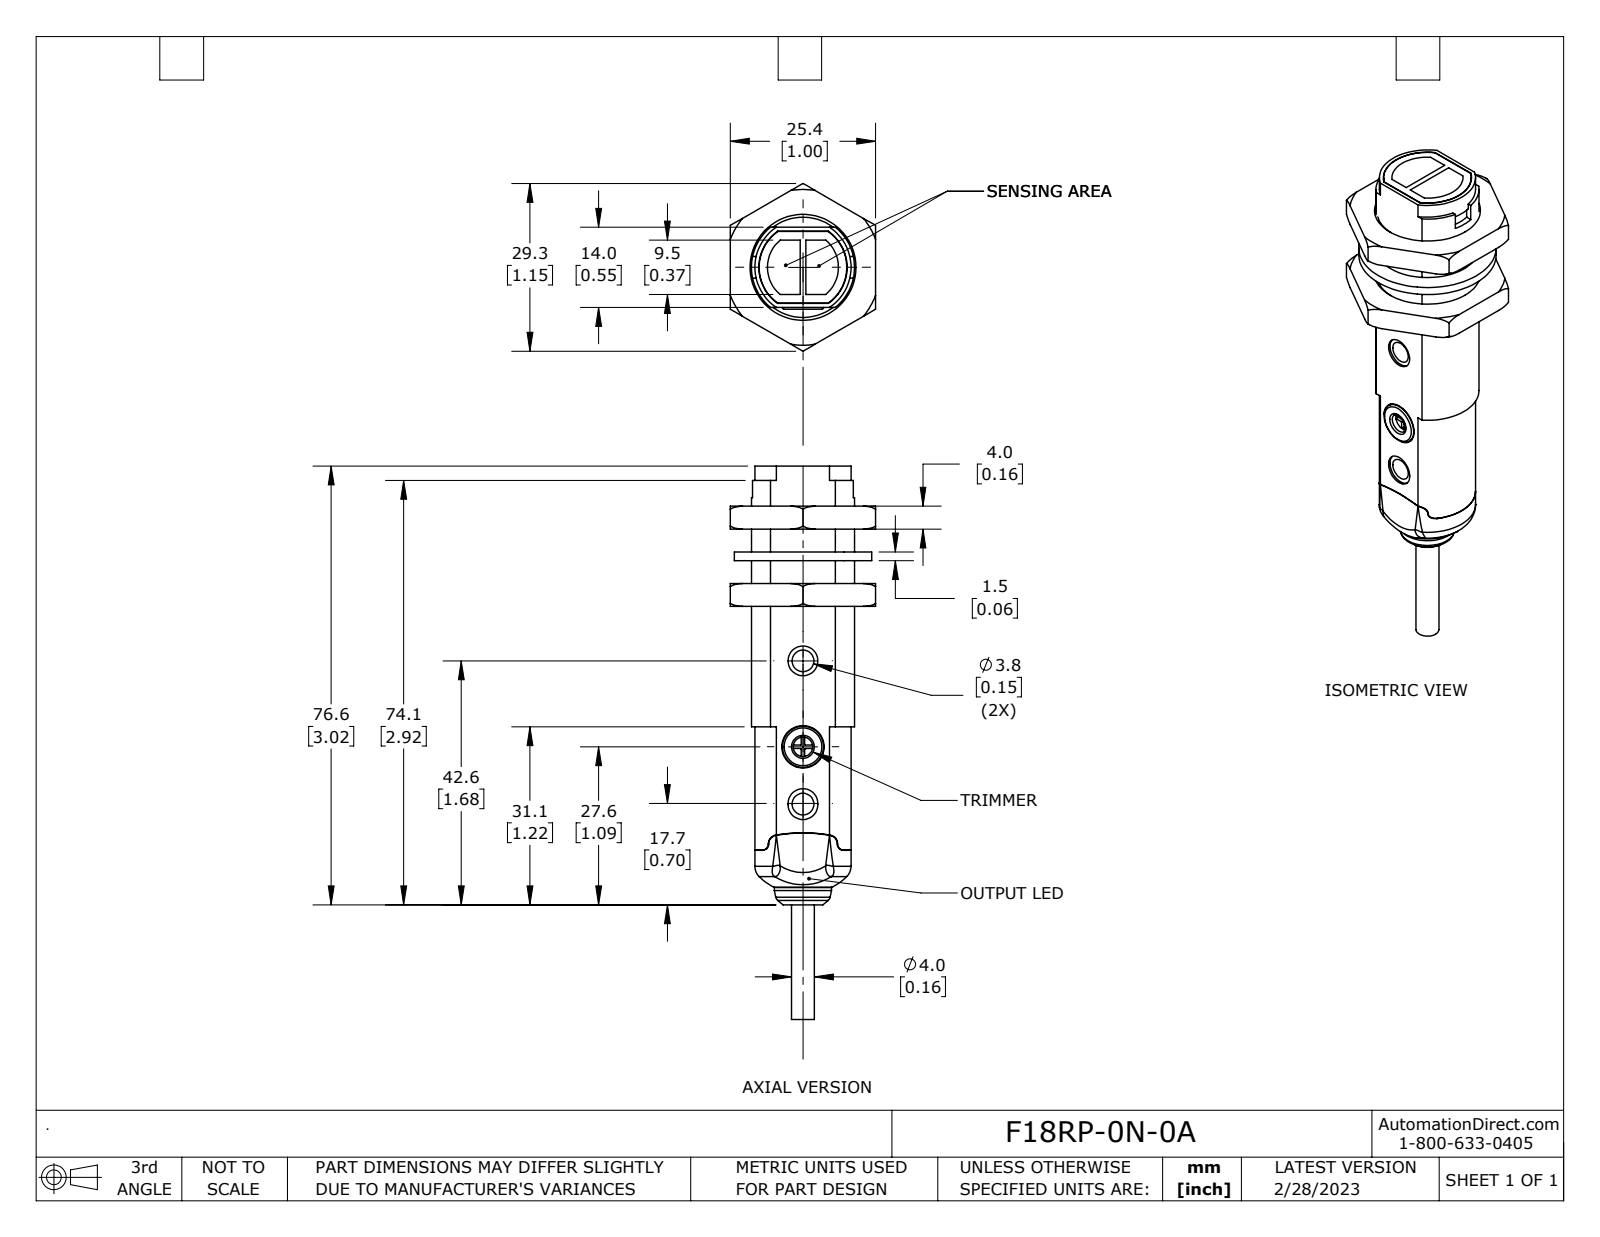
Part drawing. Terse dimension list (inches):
name: F18RP-BP-0A
written by: SolidWorks 2021 (AUTOMOTIVE_DESIGN)
unit: in
bodies: 4 solids, 178 faces (78 planar, 51 cylindrical, 49 other)
size: 3.802 × 1.153 × 0.998
volume: 1.134 in³; area: 12.48 in²
holes: 2× ⌀0.15, 1× ⌀0.134, 1× ⌀0.205, 1× ⌀0.291, 1× ⌀0.689
bosses: 1× ⌀0.945, 1× ⌀0.709, 1× ⌀0.394, 1× ⌀0.283, 1× ⌀0.157
rounds: 4× R0.039, 4× R0.059, 2× R0.102, 2× R1.102, 1× R0.02, 1× R0.301, 1× R0.303, 1× R0.307
face distances: 0.157, 0.374, 0.551, 0.531, 0.217, 0.315, 0.998, 0.689, 0.433, 0.059
hole spacings: 0.394, 0.591, 0.984
